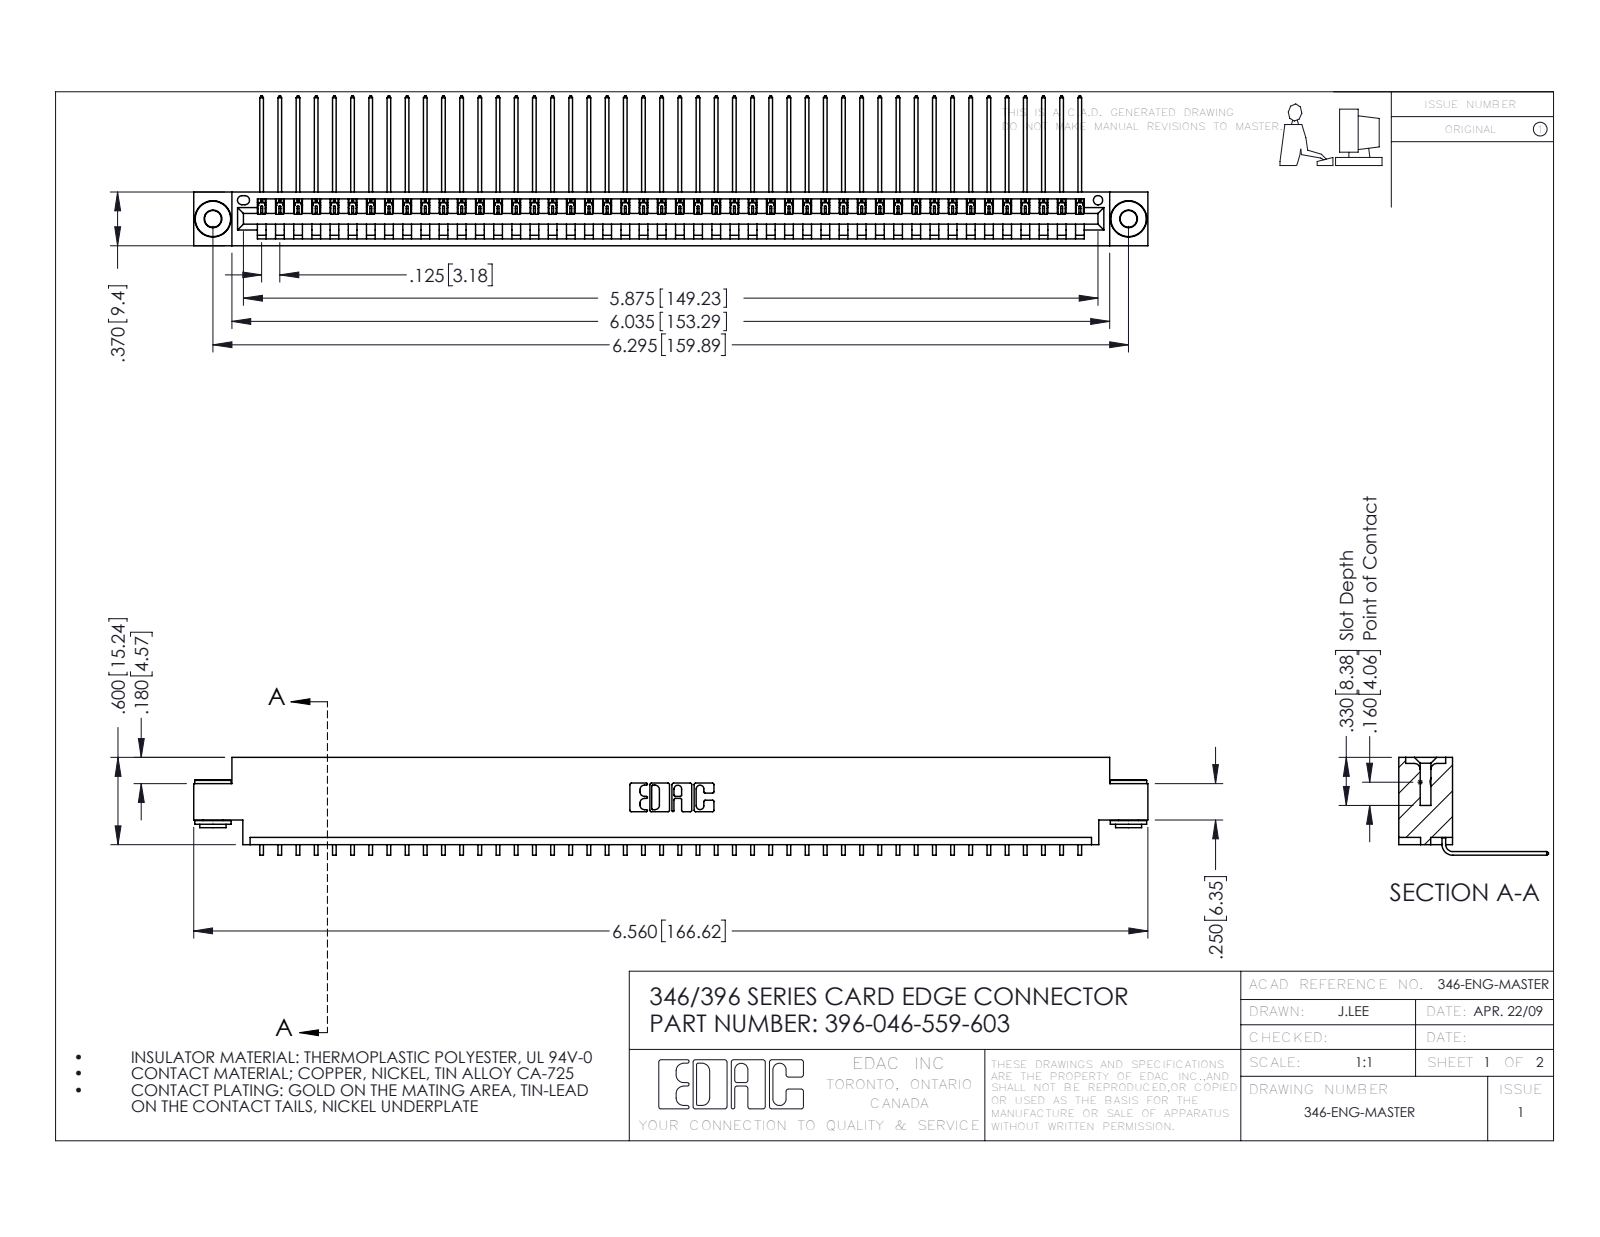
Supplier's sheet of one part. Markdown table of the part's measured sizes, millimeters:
| quantity | value |
| --- | --- |
| part name | 396-046-559-603; 345-292-001_558 559 Tail - 1; 346 Part_0.170 Offset - 0.156 Dia-TH; 345-250-002_345-250-002-102 |
| STEP written by | SolidWorks 2016 (CONFIG_CONTROL_DESIGN) |
| units | millimeters |
| bodies | 49 solids, 2924 faces (2022 planar, 894 cylindrical, 8 other) |
| overall size | 166.6 × 26.2 × 17.1 |
| volume | 16 000 mm³ |
| surface area | 21 330 mm² |
| round holes (diameter × count) | 2.9 × 2, 4 × 2, 1.6 × 1 |
| round bosses / shafts (diameter × count) | 6.4 × 2, 4.6 × 2, 3.5 × 2 |
| partial cylindrical surfaces (radius × count) | 0.2 × 92, 0.3 × 22, 0.2 × 6, 0.8 × 6, 0.7 × 3, 0.8 × 2, 1 × 2, 0.4 × 1 |
| main face-to-face distances | 1.2, 8.2, 9.4, 0.6, 6.4, 1.8, 7.6, 3.8, 5.6, 2.5 |
| hole center spacings | 6.2, 154.6, 159.9 |
